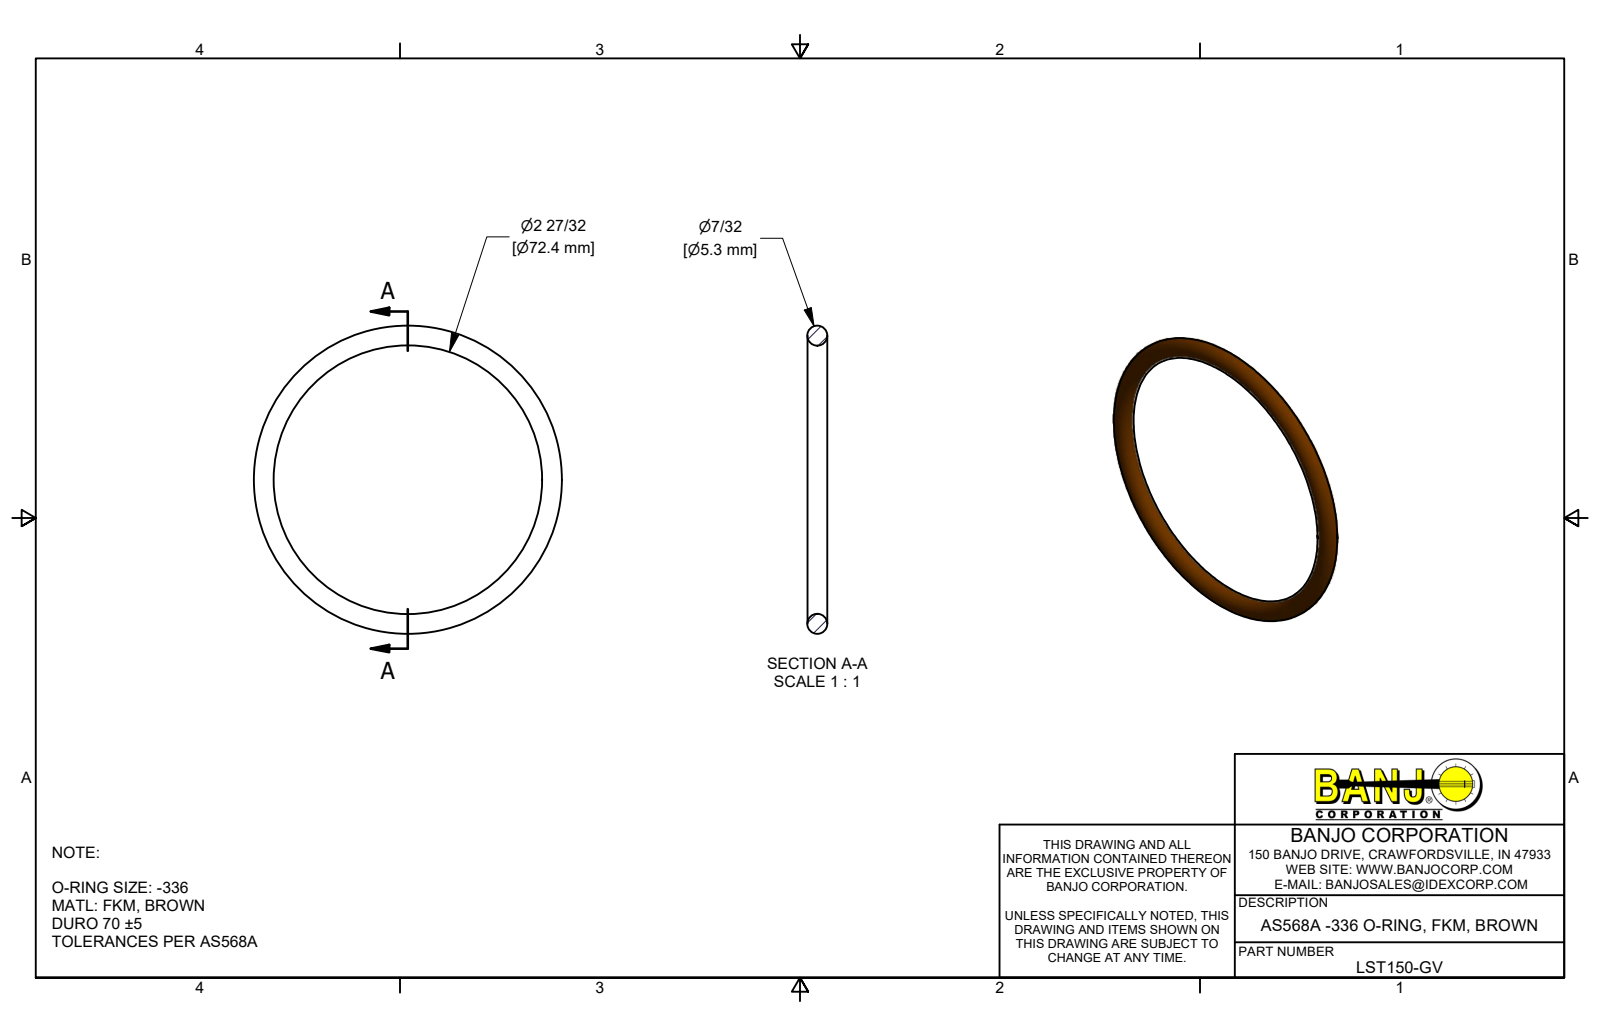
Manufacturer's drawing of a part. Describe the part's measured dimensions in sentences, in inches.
The part is named "LST150-GV". Its 3-D file was written by "Autodesk Inventor 2019 (AUTOMOTIVE_DESIGN)". It is 1 solid with 1 faces: 0 planar, 0 cylindrical and 1 other. Overall it measures 3.27 by 3.27 by 0.21 inches. Its volume is 0.333 cubic inches and its surface area 6.342 square inches.
